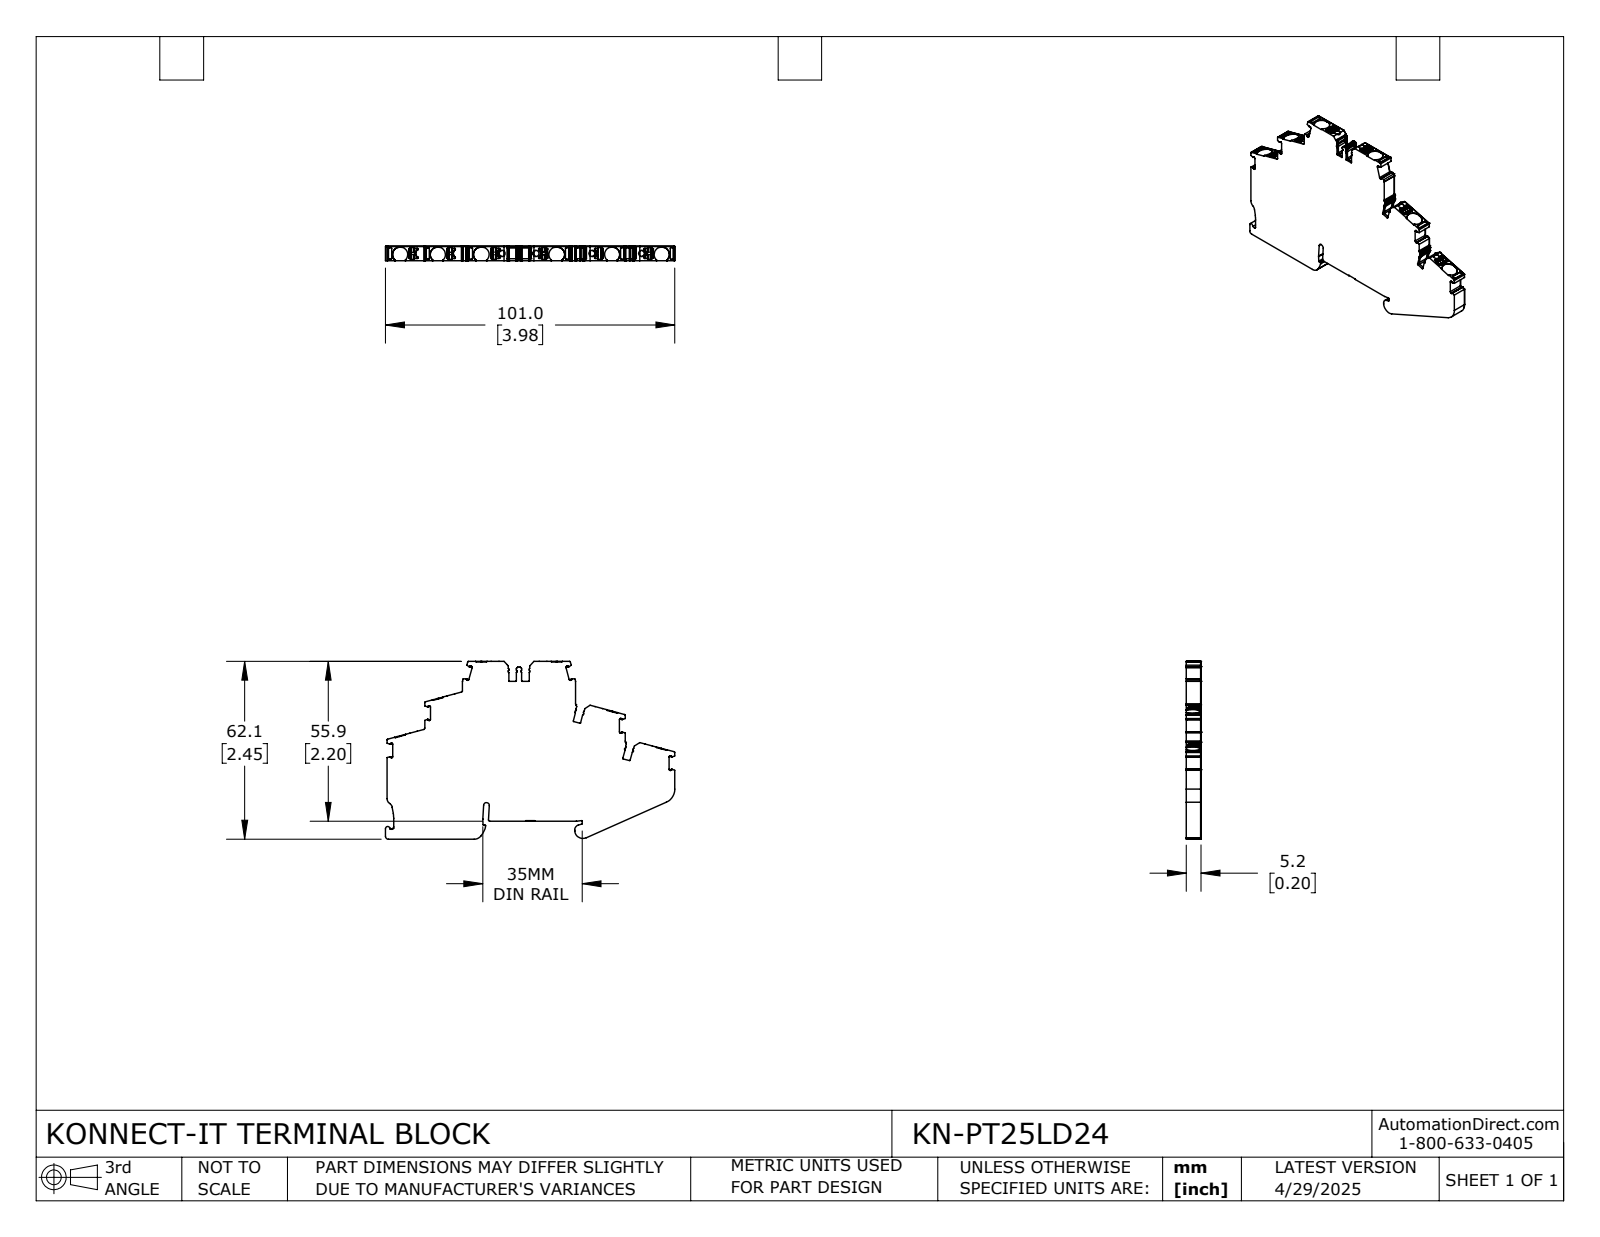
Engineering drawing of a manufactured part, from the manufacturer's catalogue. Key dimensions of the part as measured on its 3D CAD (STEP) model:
Part name (STEP PRODUCT): KN-PT25LD24
STEP written by: SolidWorks 2024 (CONFIG_CONTROL_DESIGN)
Units: inches
Bodies: 1 solid, 1212 faces (579 planar, 528 cylindrical, 105 other)
Overall size (bounding box): 3.977 × 2.445 × 0.203
Volume: 1.354 in³ · Surface area: 16.76 in²
Round holes (diameter × count): ⌀0.083 ×4
Partial cylindrical surfaces — rounded edges, fillets, slot ends (radius × count): R0.008 ×128, R0.004 ×49, R0.012 ×47, R0.02 ×26, R0.006 ×24, R0.016 ×17, R0.024 ×14, R0.006 ×12
Main face-to-face distances: 0.203, 0.246, 0.079, 2.191, 2.437, 0.319, 0.682, 0.519, 2.445, 2.199
Hole centre spacings: 0.466, 0.792
